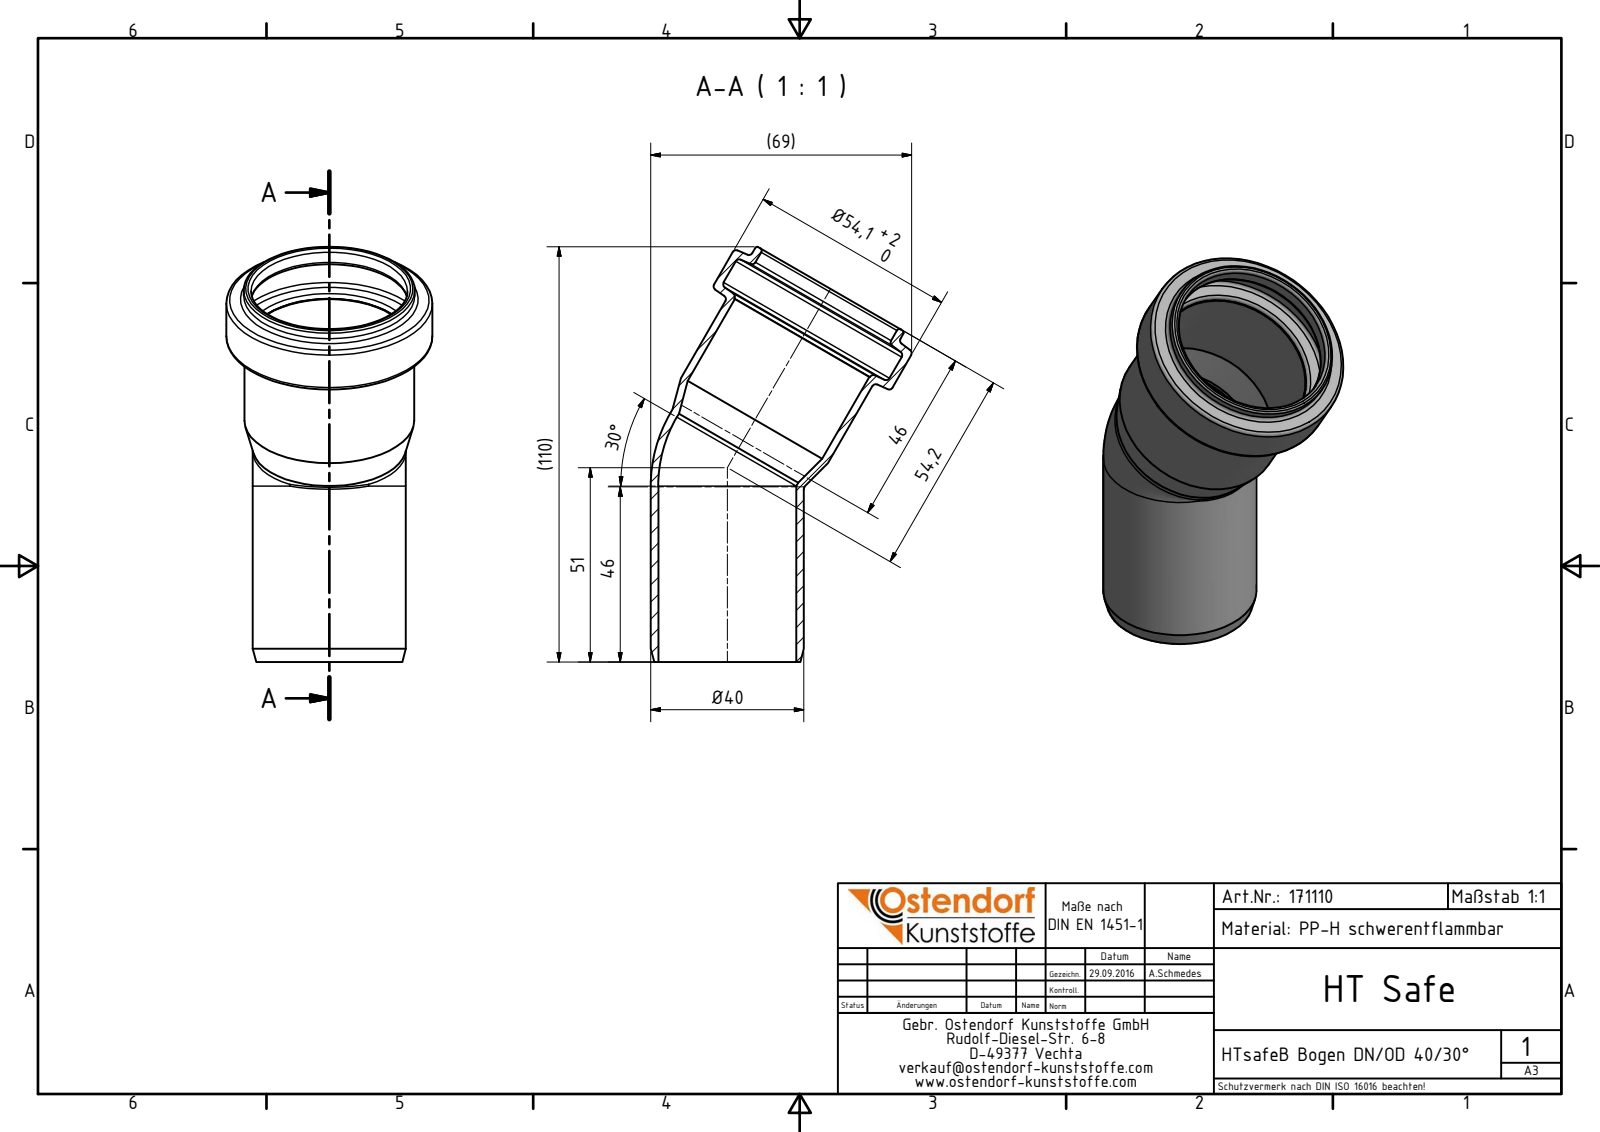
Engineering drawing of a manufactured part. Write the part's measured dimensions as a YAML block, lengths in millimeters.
part_name: "171110 HTsafeB DN_OD 40_30°"
step_written_by: "Autodesk Inventor 2016 (AUTOMOTIVE_DESIGN)"
units: millimeters
bodies: {solids: 1, faces: 34, planar: 3, cylindrical: 11, other: 20}
overall_size: [108.98, 68.52, 54.1]
volume: 28424
surface_area: 29579
round_holes:
  - {diameter: 36.2, count: 2}
  - {diameter: 40.8, count: 1}
  - {diameter: 41.1, count: 1}
  - {diameter: 50.3, count: 1}
round_bosses_or_shafts:
  - {diameter: 40.2, count: 2}
  - {diameter: 54.1, count: 1}
  - {diameter: 44.9, count: 1}
  - {diameter: 44.6, count: 1}
face_to_face_distances: [14.91]
